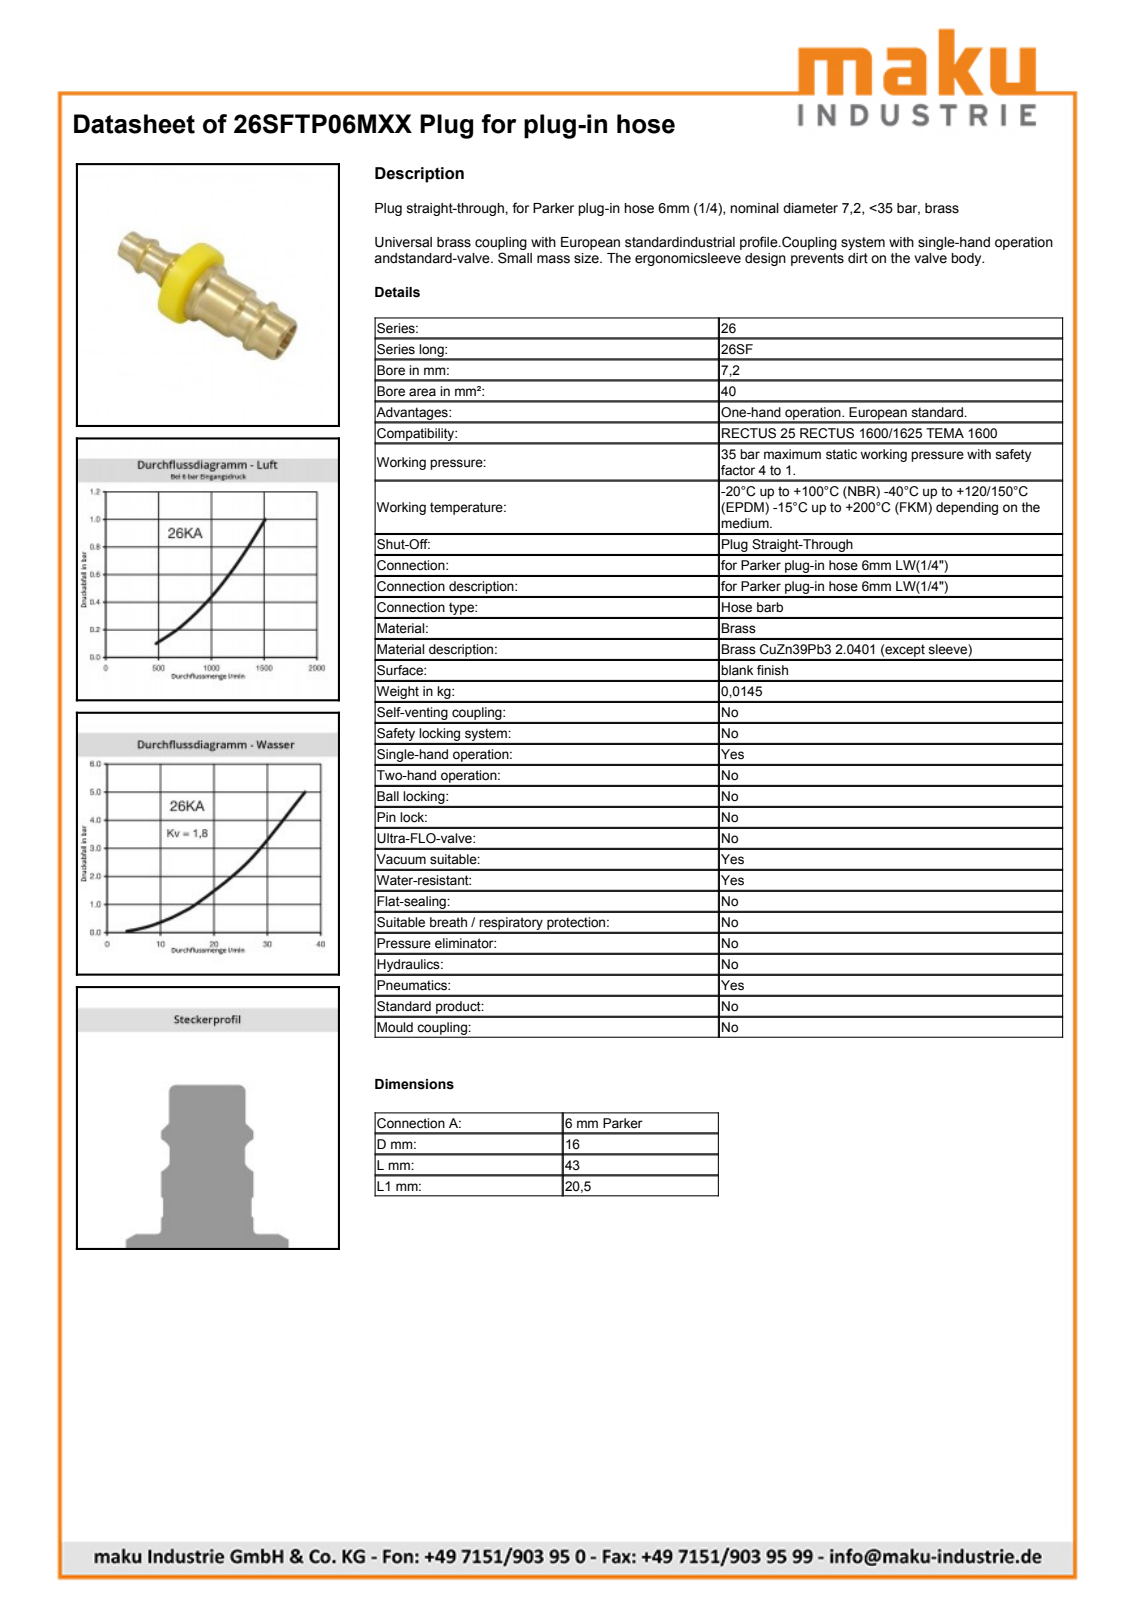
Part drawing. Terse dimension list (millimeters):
name: D105985; D105976; D105982
written by: Autodesk Inventor 2011 (AUTOMOTIVE_DESIGN)
unit: mm
bodies: 2 solids, 40 faces (10 planar, 15 cylindrical, 15 other)
size: 42.5 × 17.4 × 17.4
volume: 2 095 mm³; area: 3 173 mm²
holes: 1× ⌀4.95, 1× ⌀7.85, 1× ⌀8.1, 1× ⌀15
bosses: 1× ⌀17.4, 1× ⌀14, 1× ⌀12, 1× ⌀10, 1× ⌀9.75, 1× ⌀8.68, 1× ⌀7.87, 1× ⌀6.6
face distances: 1.2, 3.2, 4.4, 3.56, 6.76, 7.96, 6.22, 10.06, 6.5, 3.3
